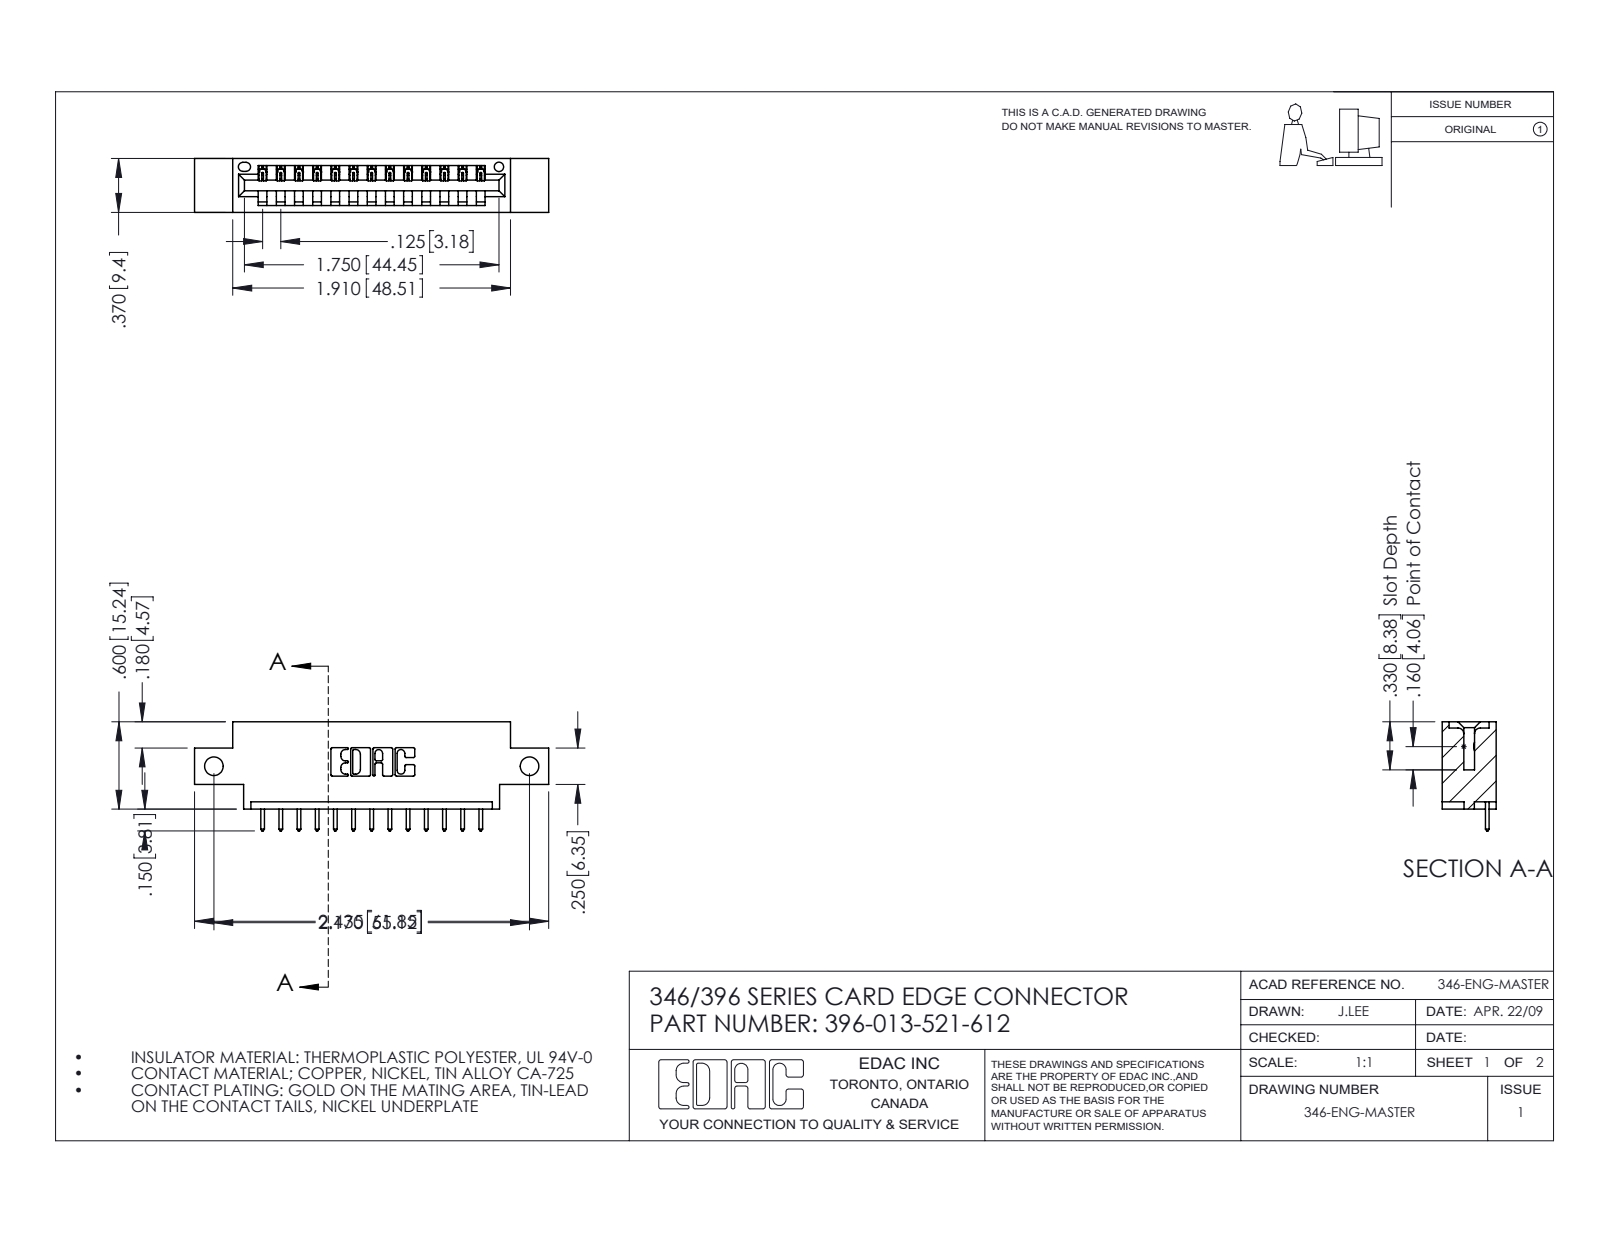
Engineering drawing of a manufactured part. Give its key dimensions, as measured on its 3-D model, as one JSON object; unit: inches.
{"part_name": "396-013-521-612; 345-292-001_345-293-121; 346 Part_0.170 Offset - Side Mount", "step_written_by": "SolidWorks 2016 (CONFIG_CONTROL_DESIGN)", "units": "inches", "bodies": {"solids": 14, "faces": 880, "planar": 600, "cylindrical": 280, "other": 0}, "overall_size": [2.435, 0.75, 0.37], "volume_in3": 0.332, "surface_area_in2": 9.852, "round_holes": [[0.128, 2], [0.064, 1]], "partial_cylinders_radius": [[0.006, 26], [0.01, 26], [0.01, 22], [0.007, 6], [0.031, 6], [0.026, 3], [0.031, 2], [0.04, 2]], "face_to_face_distances": [0.37, 0.25, 0.048, 0.322, 0.148, 0.072, 0.298, 0.025, 0.222, 0.1], "hole_center_spacings": [2.17]}
